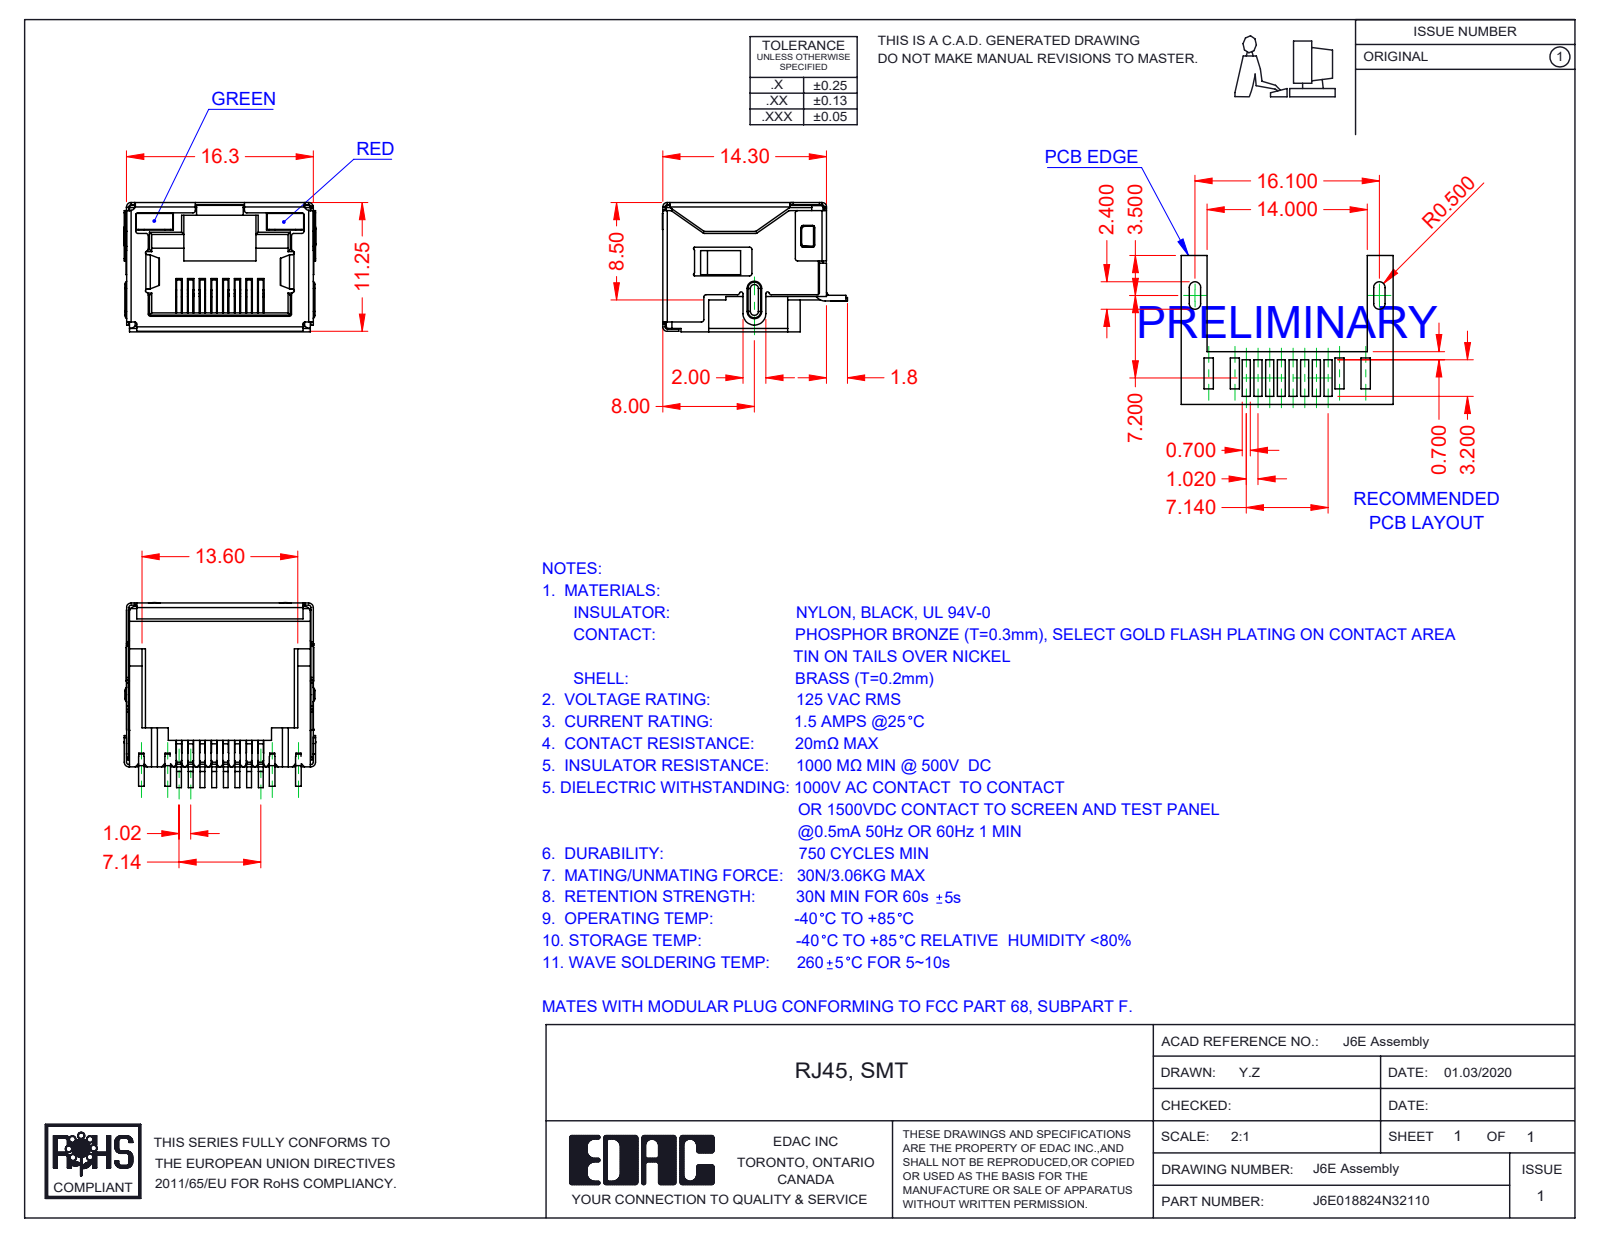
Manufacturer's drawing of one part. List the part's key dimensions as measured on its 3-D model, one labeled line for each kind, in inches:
Part name (STEP PRODUCT): 6E Contacts; 6E LED RH_2-Red; 6E LED LH_3-Green; 6E Shield_LED (+2 more)
STEP written by: SolidWorks 2016 (CONFIG_CONTROL_DESIGN)
Units: inches
Bodies: 12 solids, 1496 faces (1099 planar, 347 cylindrical, 50 other)
Overall size (bounding box): 0.659 × 0.636 × 0.445
Volume: 0.068 in³ · Surface area: 6.27 in²
Partial cylindrical surfaces — rounded edges, fillets, slot ends (radius × count): R0.008 ×82, R0.01 ×17, R0.016 ×13, R0.02 ×13, R0.004 ×10, R0.006 ×7, R0.012 ×4, R0.039 ×3
Main face-to-face distances: 0.435, 0.632, 0.634, 0.624, 0.437, 0.445, 0.094, 0.028, 0.388, 0.019
